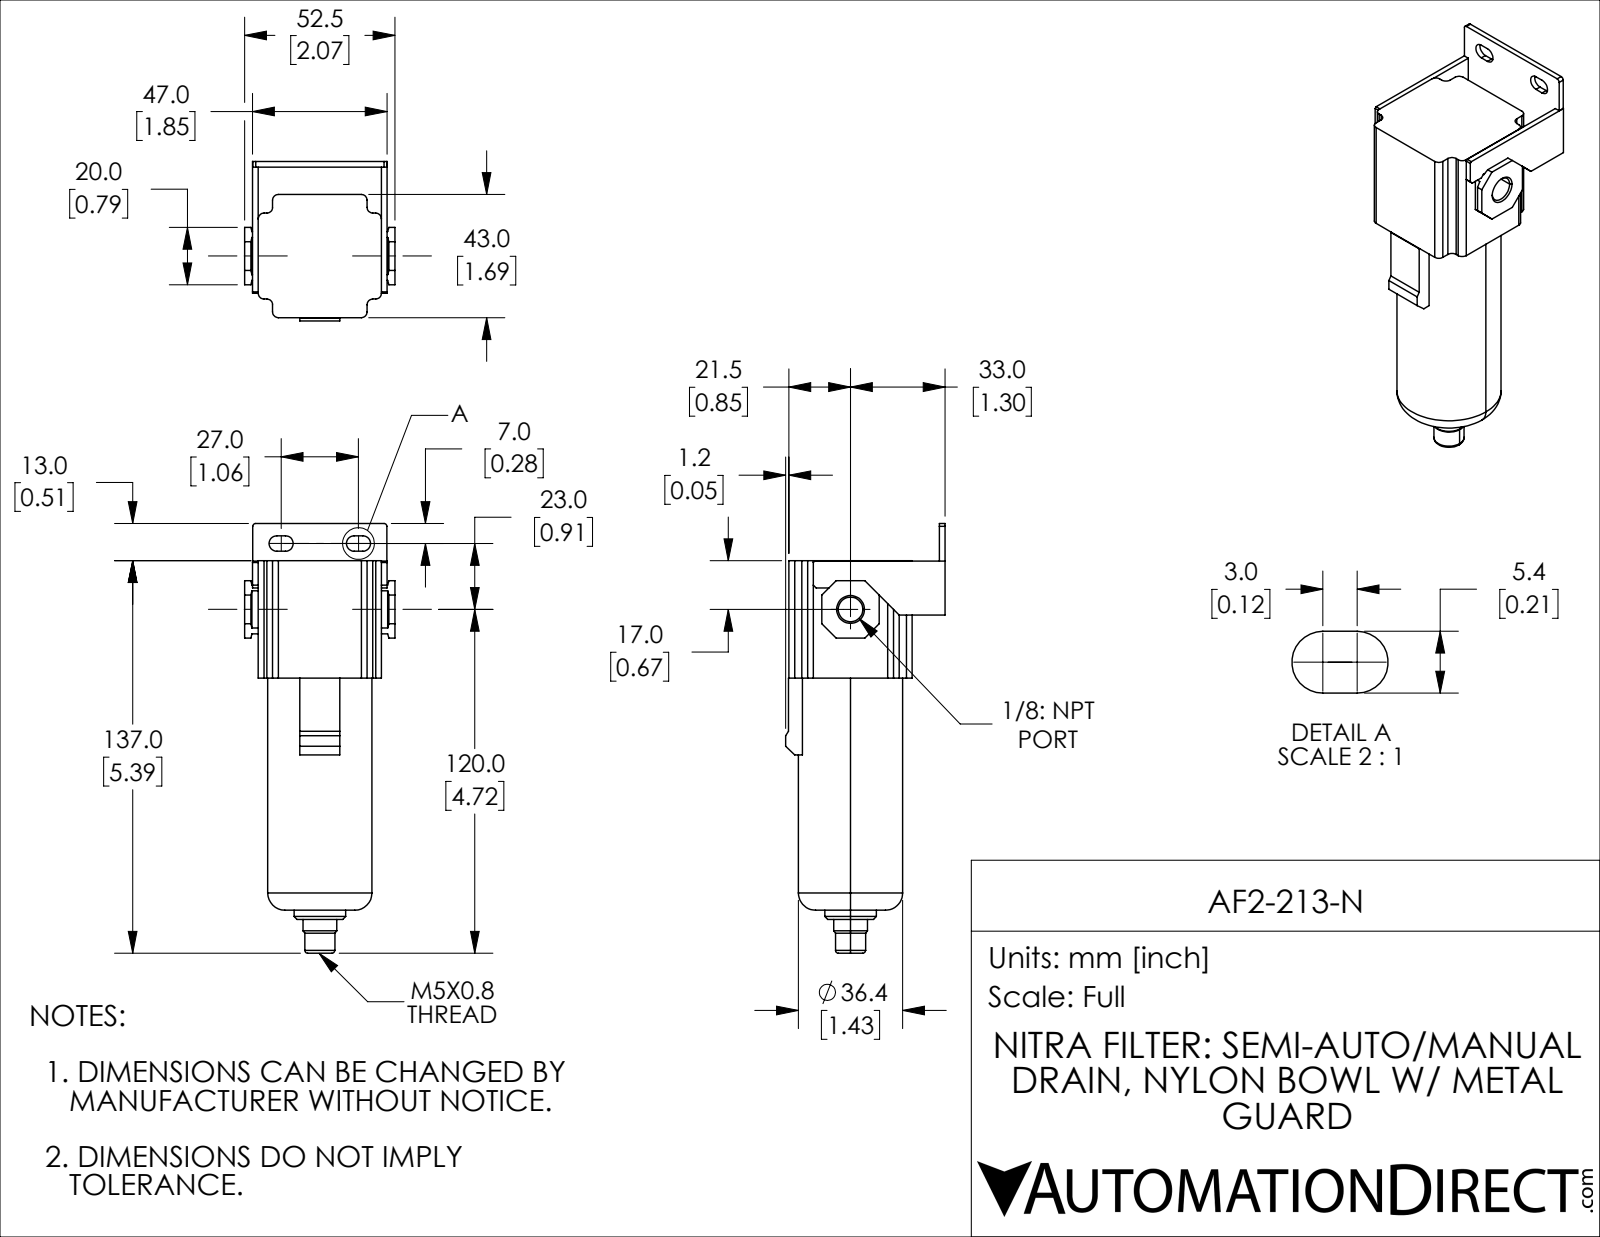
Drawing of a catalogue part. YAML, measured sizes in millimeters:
part_name: "AF2-213-N"
step_written_by: "SolidWorks 2019 (CONFIG_CONTROL_DESIGN)"
units: millimeters
bodies: {solids: 1, faces: 136, planar: 90, cylindrical: 32, other: 14}
overall_size: [150, 55.67, 52.5]
volume: 164143
surface_area: 26027
round_holes:
  - {diameter: 4.13, count: 1}
  - {diameter: 8.57, count: 1}
round_bosses_or_shafts:
  - {diameter: 36.4, count: 1}
  - {diameter: 18, count: 1}
  - {diameter: 11.8, count: 1}
  - {diameter: 10.5, count: 1}
partial_cylinders:
  - {radius: 2, count: 12}
  - {radius: 2.7, count: 4}
  - {radius: 1, count: 2}
face_to_face_distances: [2, 43, 9.5, 52.5, 11.5, 45, 54.5, 41, 47, 2.75]
